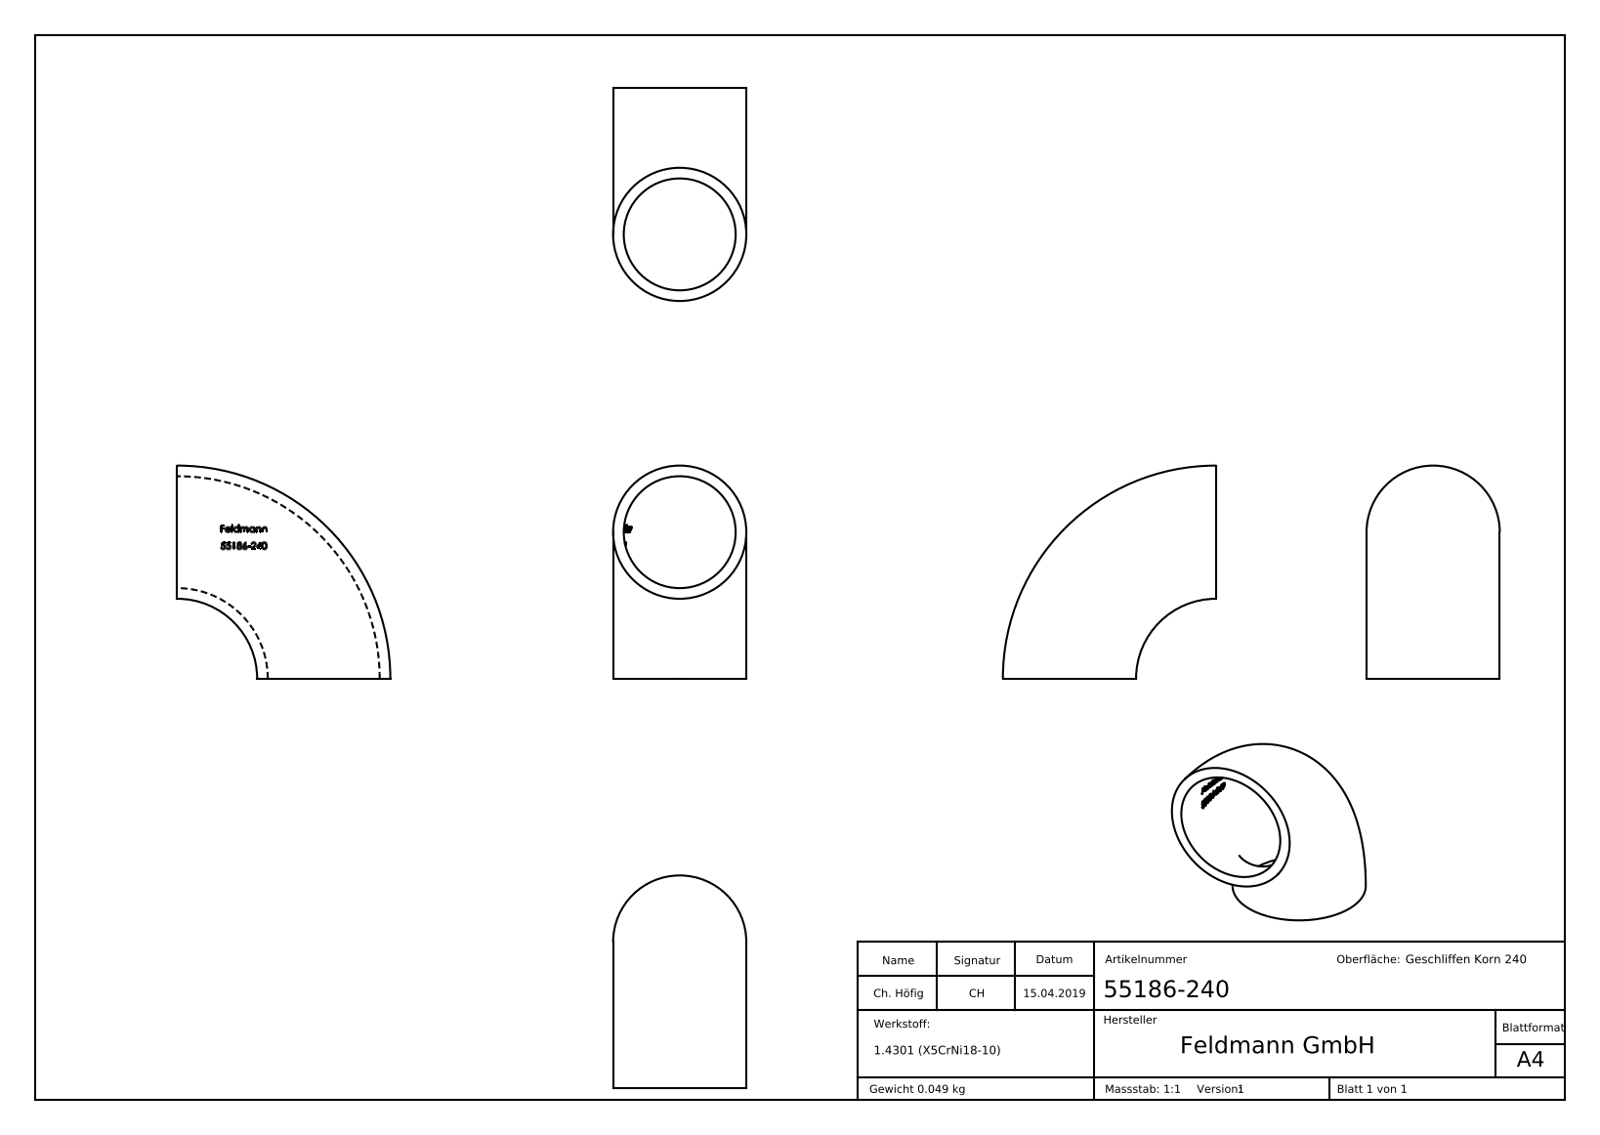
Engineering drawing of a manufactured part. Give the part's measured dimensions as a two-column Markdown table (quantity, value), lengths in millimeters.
| quantity | value |
| --- | --- |
| part name | 55186-240 |
| STEP written by | SolidWorks 2015 (CONFIG_CONTROL_DESIGN) |
| units | millimeters |
| bodies | 1 solid, 234 faces (100 planar, 0 cylindrical, 134 other) |
| overall size | 40 × 40 × 25 |
| volume | 6 242 mm³ |
| surface area | 6 541 mm² |
| main face-to-face distances | 0.39, 1.26, 2.97, 4.23, 3.66, 2.02, 3.27, 1.32, 2.4, 0.88 |
